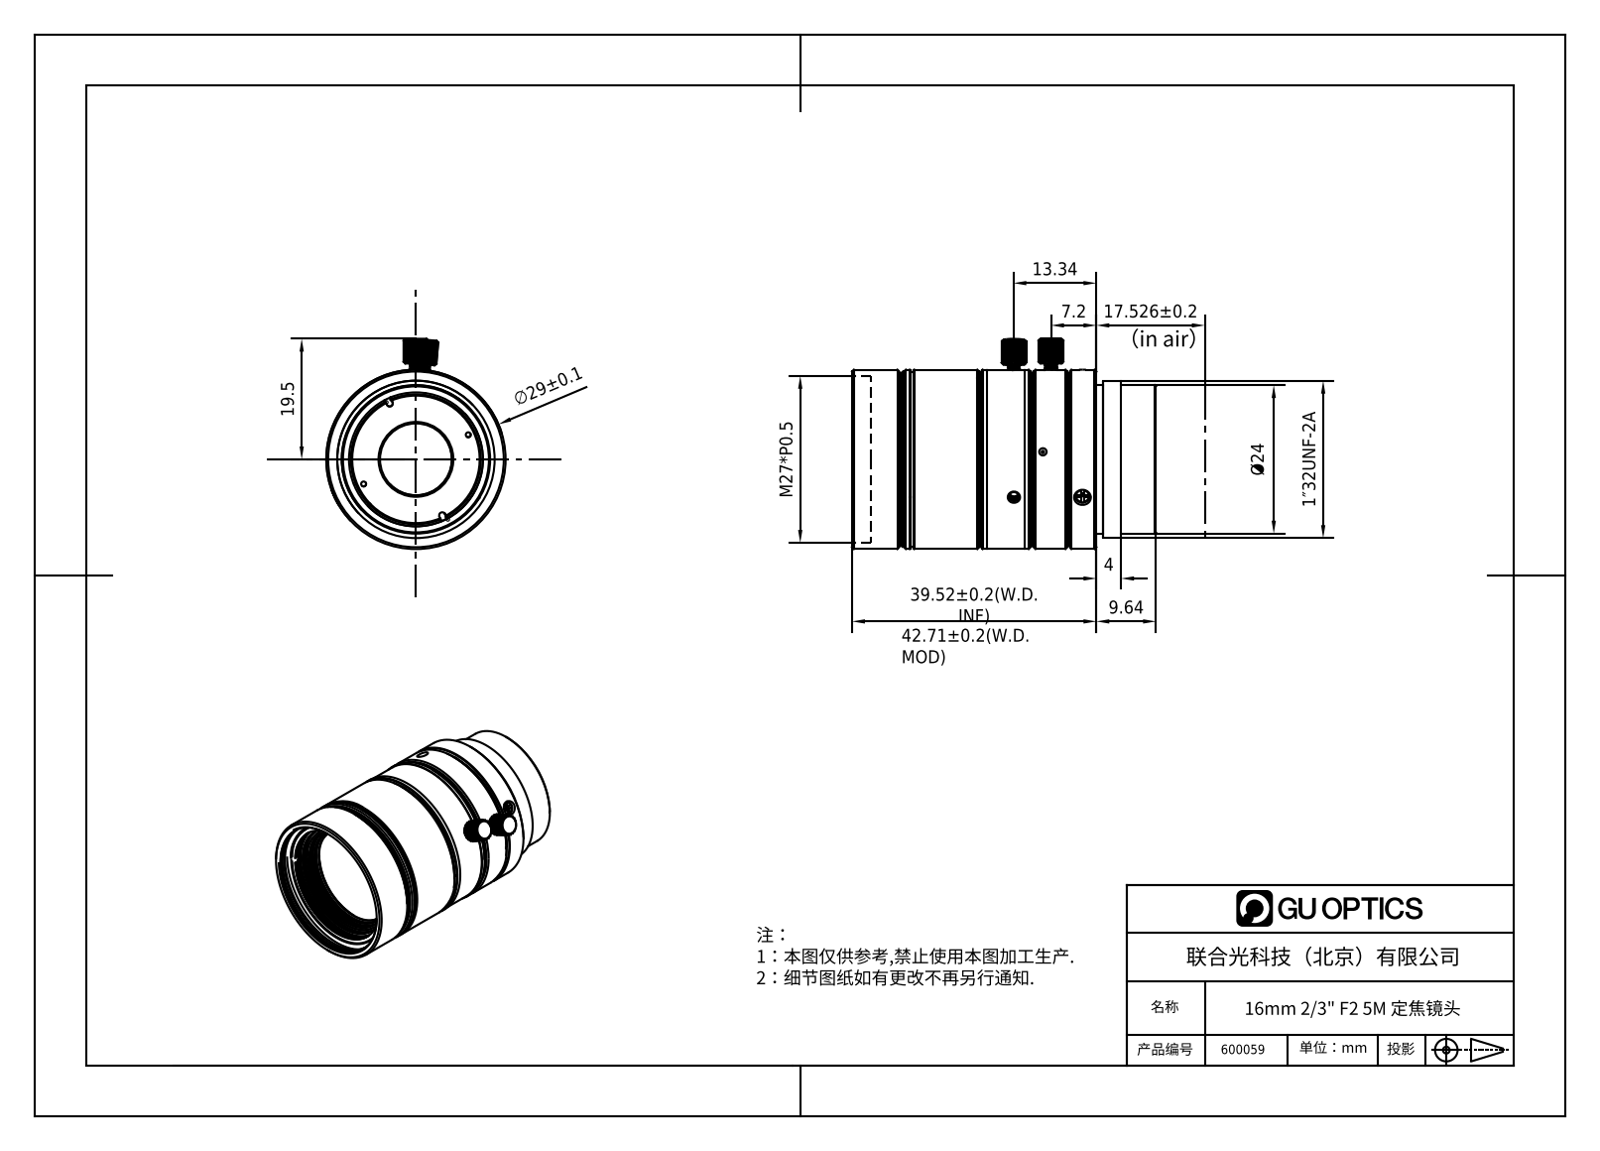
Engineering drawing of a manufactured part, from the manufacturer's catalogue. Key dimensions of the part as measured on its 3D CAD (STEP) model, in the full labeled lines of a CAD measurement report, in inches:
Part name (STEP PRODUCT): 600059
STEP written by: SolidWorks 2020 (CONFIG_CONTROL_DESIGN)
Units: inches
Bodies: 6 solids, 1018 faces (273 planar, 493 cylindrical, 252 other)
Overall size (bounding box): 1.935 × 1.294 × 1.142
Volume: 1.607 in³ · Surface area: 19.38 in²
Round holes (diameter × count): ⌀0.067 ×3, ⌀0.087 ×3, ⌀0.106 ×3, ⌀0.031 ×2, ⌀0.063 ×2, ⌀0.079 ×2, ⌀0.457 ×1, ⌀0.524 ×1, ⌀0.654 ×1, ⌀0.752 ×1, ⌀0.774 ×1, ⌀0.807 ×1
Round bosses / shafts (diameter × count): ⌀0.063 ×5, ⌀0.098 ×3, ⌀0.047 ×3, ⌀0.079 ×2, ⌀1.142 ×1, ⌀1.134 ×1, ⌀1.11 ×1, ⌀1.102 ×1
Partial cylindrical surfaces — rounded edges, fillets, slot ends (radius × count): R0.044 ×6, R0.133 ×6, R0.135 ×6, R0.008 ×2, R0.02 ×2, R0.044 ×2, R0.079 ×2, R0.485 ×1
Main face-to-face distances: 0.378, 1.256, 0.317, 0.543, 1.108, 0.419, 0.939, 1.107, 0.728, 1.634
Hole centre spacings: 0.368, 0.437, 0.736
